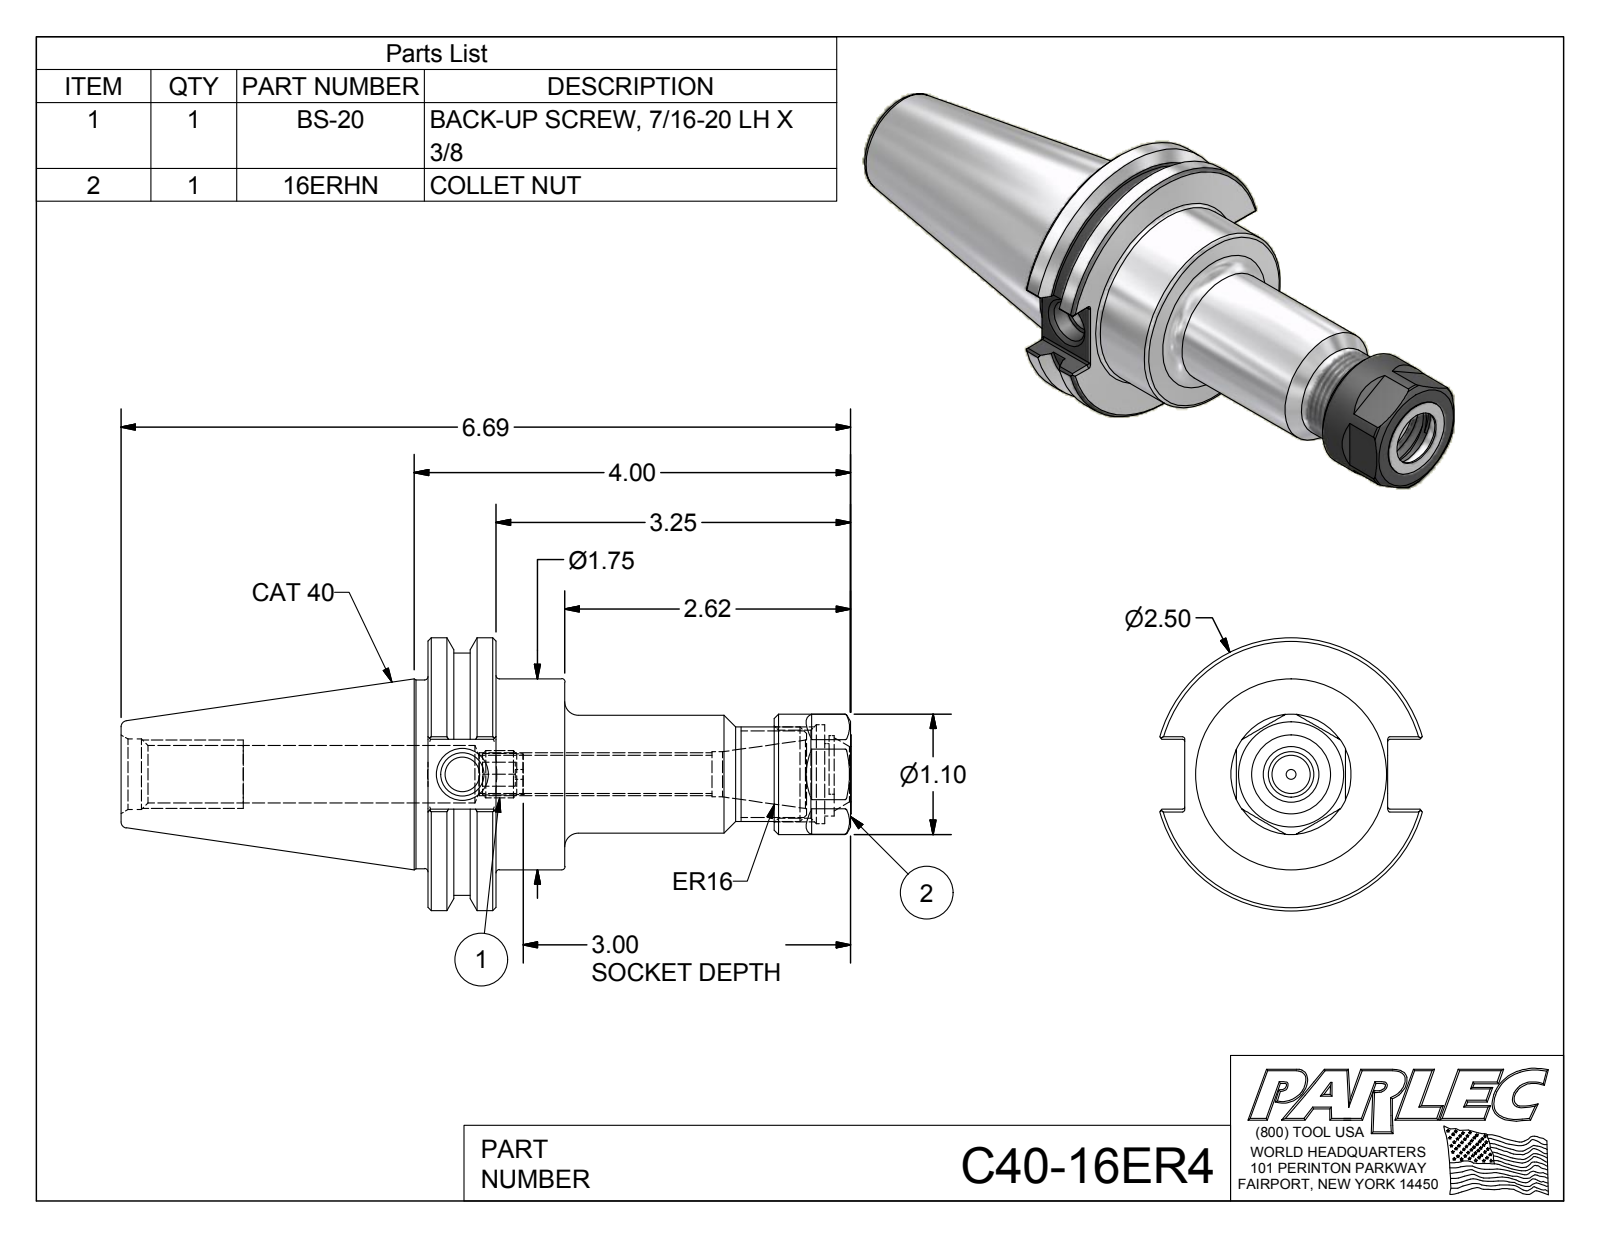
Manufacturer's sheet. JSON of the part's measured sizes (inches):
{"part_name": "C40-16ER4; C40-16ER4-1; 16ERHN; BS-20", "step_written_by": "Autodesk Inventor 2012 (AUTOMOTIVE_DESIGN)", "units": "inches", "bodies": {"solids": 3, "faces": 138, "planar": 60, "cylindrical": 39, "other": 39}, "overall_size": [6.693, 2.5, 2.403], "volume_in3": 9.438, "surface_area_in2": 51.21, "round_holes": [[0.09, 1], [0.315, 1], [0.351, 1], [0.399, 1], [0.413, 1], [0.508, 1], [0.527, 1], [0.527, 1], [0.648, 1], [0.661, 1], [0.807, 1], [0.906, 1]], "round_bosses_or_shafts": [[2.5, 1], [2.219, 1], [1.75, 1], [1.73, 1], [1.102, 1], [1.08, 1], [0.866, 1], [0.724, 1]], "partial_cylinders_radius": [[0.02, 12], [0.354, 1]], "face_to_face_distances": [0.625, 1.255, 0.63, 3.25, 0.236, 1, 3.875, 2.62, 3.639, 3.014], "hole_center_spacings": [0.051]}
